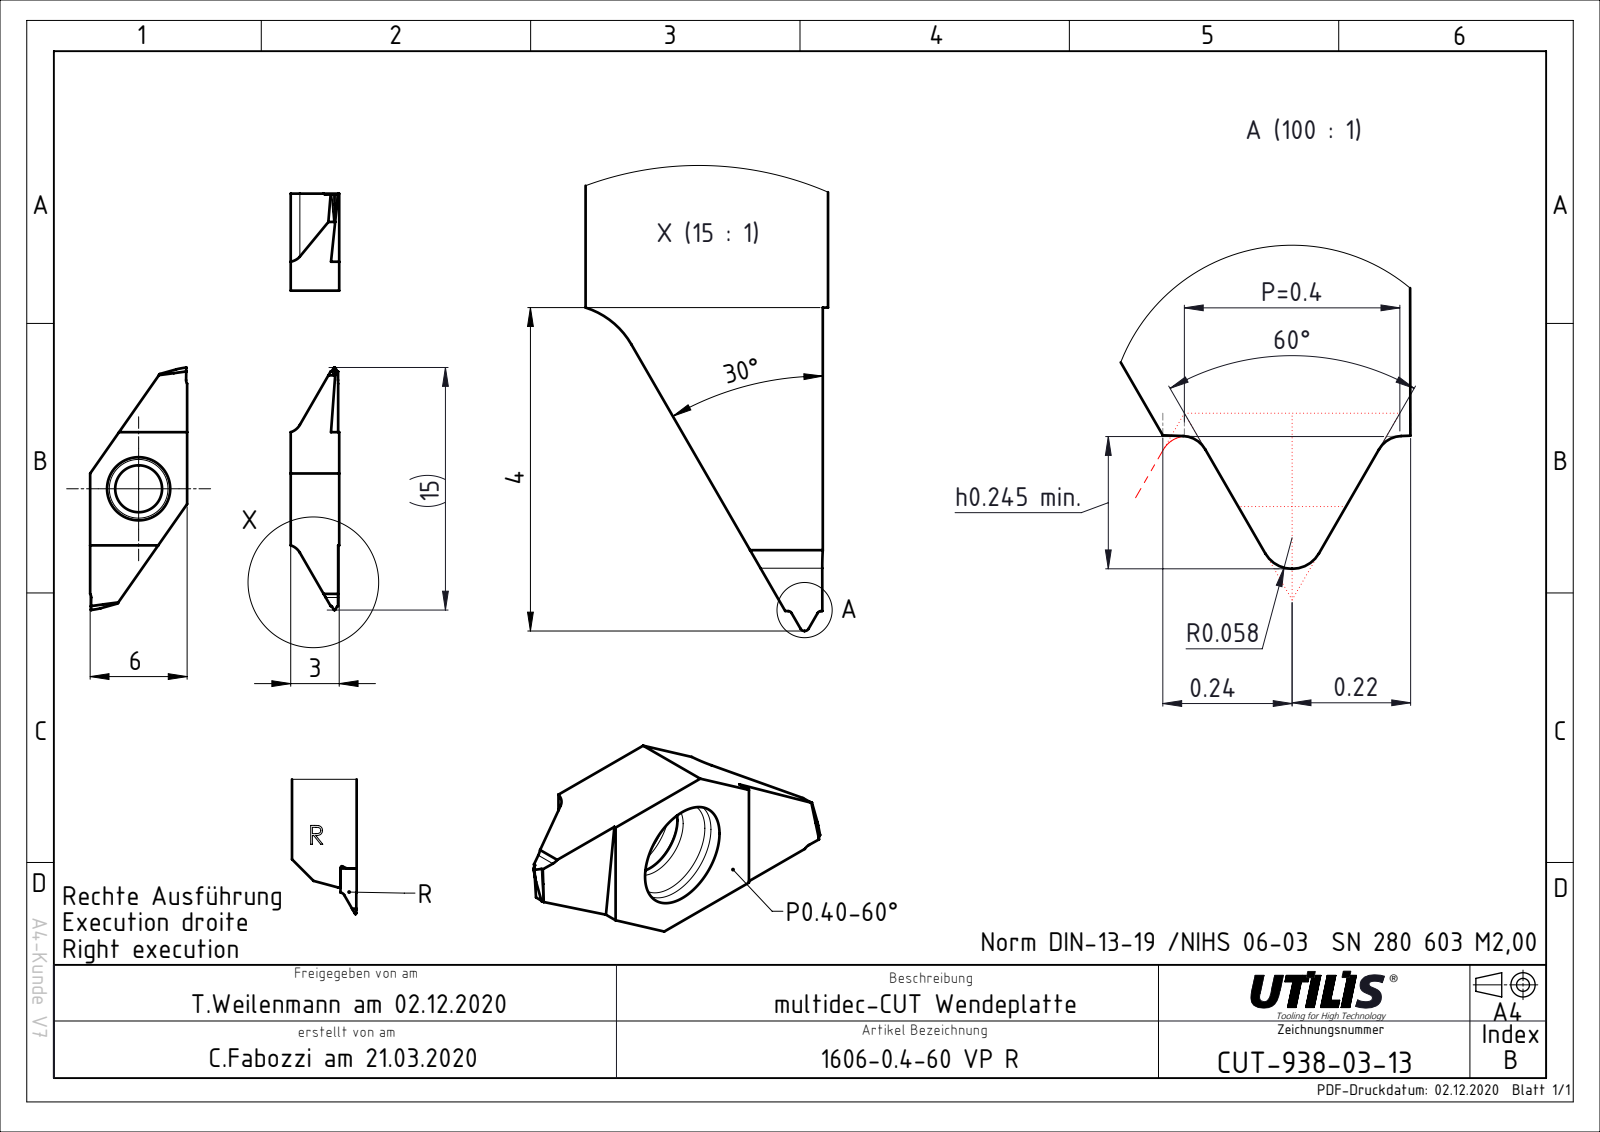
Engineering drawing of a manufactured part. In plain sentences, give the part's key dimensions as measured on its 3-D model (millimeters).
The part is named "CUT-938-03; ASME Y14.5". Its 3-D file was written by "FormatWorks Professional (AP242_MANAGED_MODEL_BASED_3D_ENGINEERING_MIM_LF)". It is 1 solid with 40 faces: 22 planar, 14 cylindrical and 4 other. Overall it measures 15 by 6 by 3 millimeters. Its volume is 129 cubic millimeters and its surface area 212 square millimeters. Round holes: 1 of diameter 2.9. Partial cylindrical surfaces (rounded edges, fillets, slot ends): 2 of radius 1. The main face-to-face distances are 6, 3, 9, 11.17, 12, 7, 13.03.
